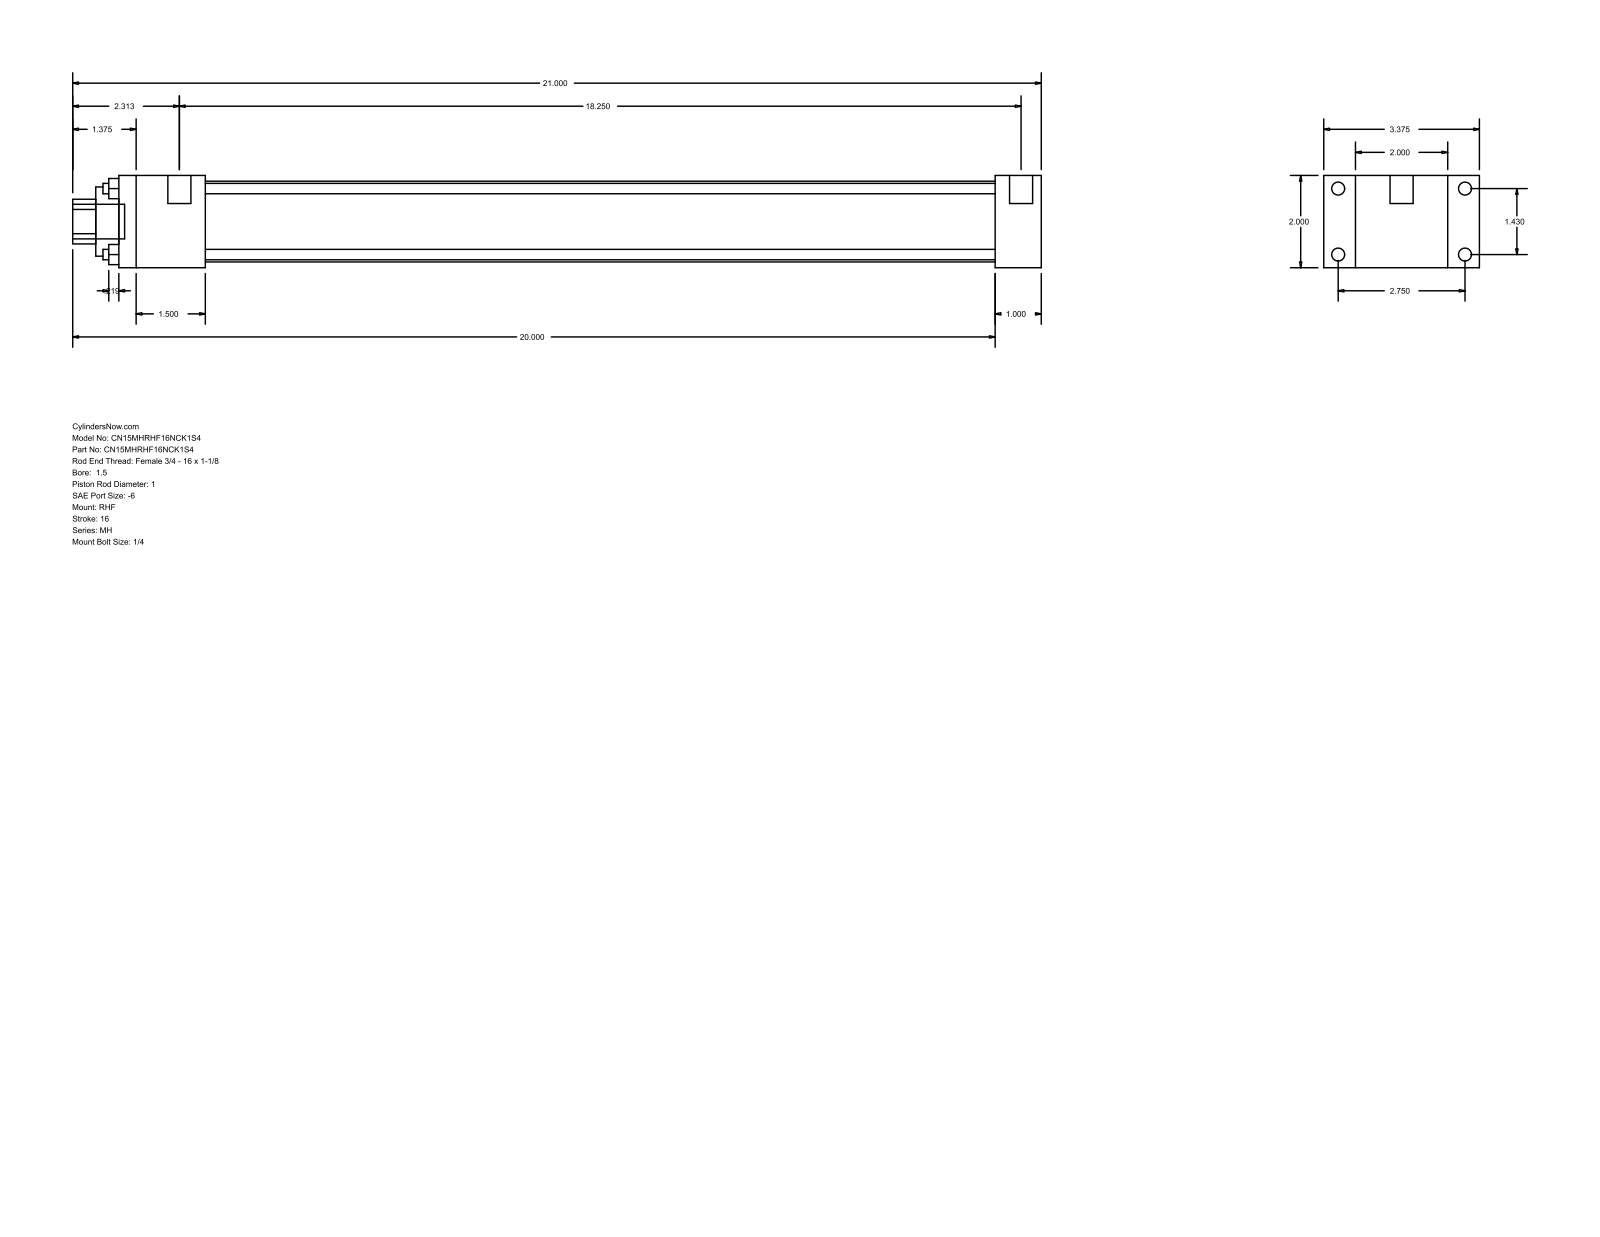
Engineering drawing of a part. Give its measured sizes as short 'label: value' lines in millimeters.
name: MH_RHF__0150_1
written by: GSSL Pune (CONFIG_CONTROL_DESIGN)
unit: mm
bodies: 0 solids, 88 faces (60 planar, 28 cylindrical, 0 other)
size: 533.4 × 85.72 × 50.8
holes: 4× ⌀5.71, 1× ⌀25.4, 1× ⌀38.1, 1× ⌀44.45
bosses: 4× ⌀7.14, 4× ⌀5.56, 2× ⌀12.7, 1× ⌀19.05
rounds: 1× R12.29
face distances: 50.8, 25.4, 17.46, 68.26, 85.72, 508, 482.6, 47.63, 434.97, 460.37
hole spacings: 25.68, 36.32, 51.36
